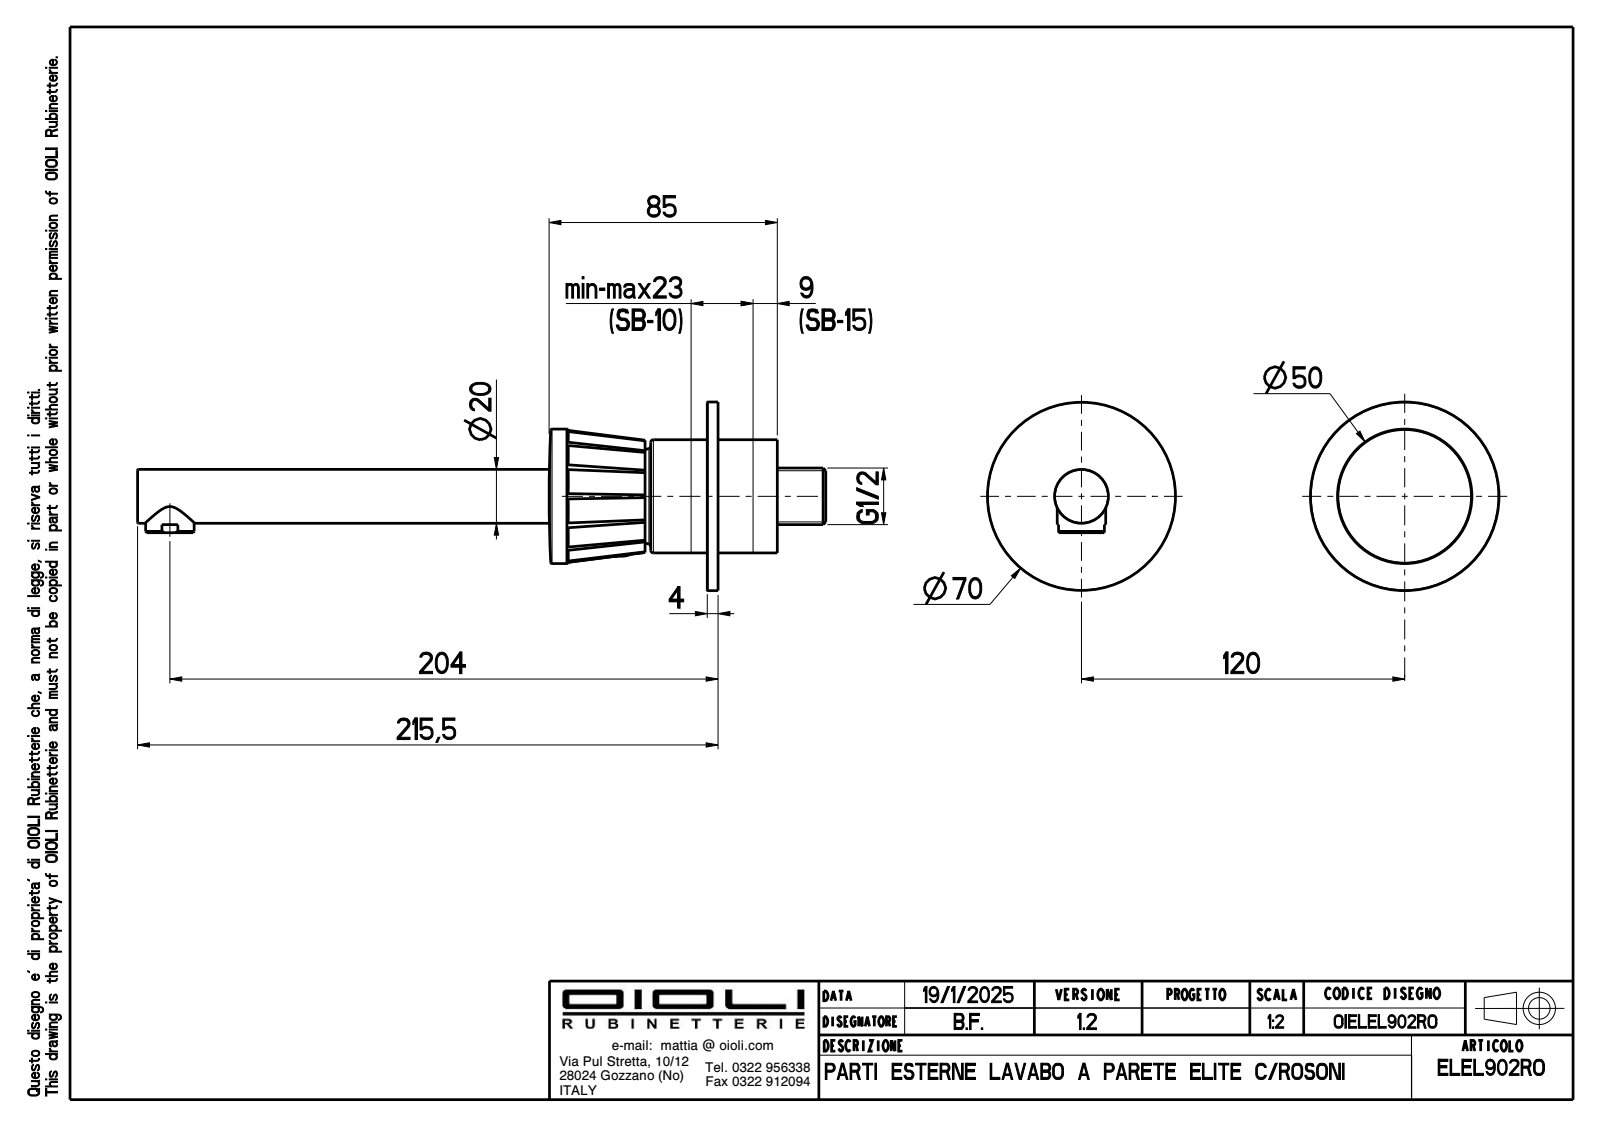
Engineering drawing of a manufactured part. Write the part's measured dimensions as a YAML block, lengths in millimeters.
part_name: "OIBR00949; OIBR00242; OIBR00144; OIBR00386 (+5 more)"
step_written_by: "CREO PARAMETRIC BY PTC INC, 2024493 (CONFIG_CONTROL_DESIGN)"
units: millimeters
bodies: {solids: 8, faces: 292, planar: 98, cylindrical: 110, other: 84}
overall_size: [237.5, 189.9, 70]
volume: 93062
surface_area: 71086
round_holes:
  - {diameter: 4.2, count: 2}
  - {diameter: 15.5, count: 2}
  - {diameter: 17, count: 2}
  - {diameter: 4, count: 1}
  - {diameter: 4.5, count: 1}
  - {diameter: 5.3, count: 1}
  - {diameter: 6.5, count: 1}
  - {diameter: 9.5, count: 1}
  - {diameter: 10, count: 1}
  - {diameter: 11, count: 1}
  - {diameter: 12.9, count: 1}
  - {diameter: 14, count: 1}
round_bosses_or_shafts:
  - {diameter: 18, count: 2}
  - {diameter: 16.5, count: 2}
  - {diameter: 5, count: 2}
  - {diameter: 70, count: 1}
  - {diameter: 69.8, count: 1}
  - {diameter: 49.9, count: 1}
  - {diameter: 42, count: 1}
  - {diameter: 31.5, count: 1}
partial_cylinders:
  - {radius: 0.1, count: 10}
  - {radius: 6.8, count: 2}
face_to_face_distances: [3.5, 0.5, 4, 59.6, 56.1, 55.6, 1.5, 24.1, 2.1, 2.6]
hole_center_spacings: [4.7, 120, 120.09, 122.4, 122.46, 192, 206.13, 206.37]
